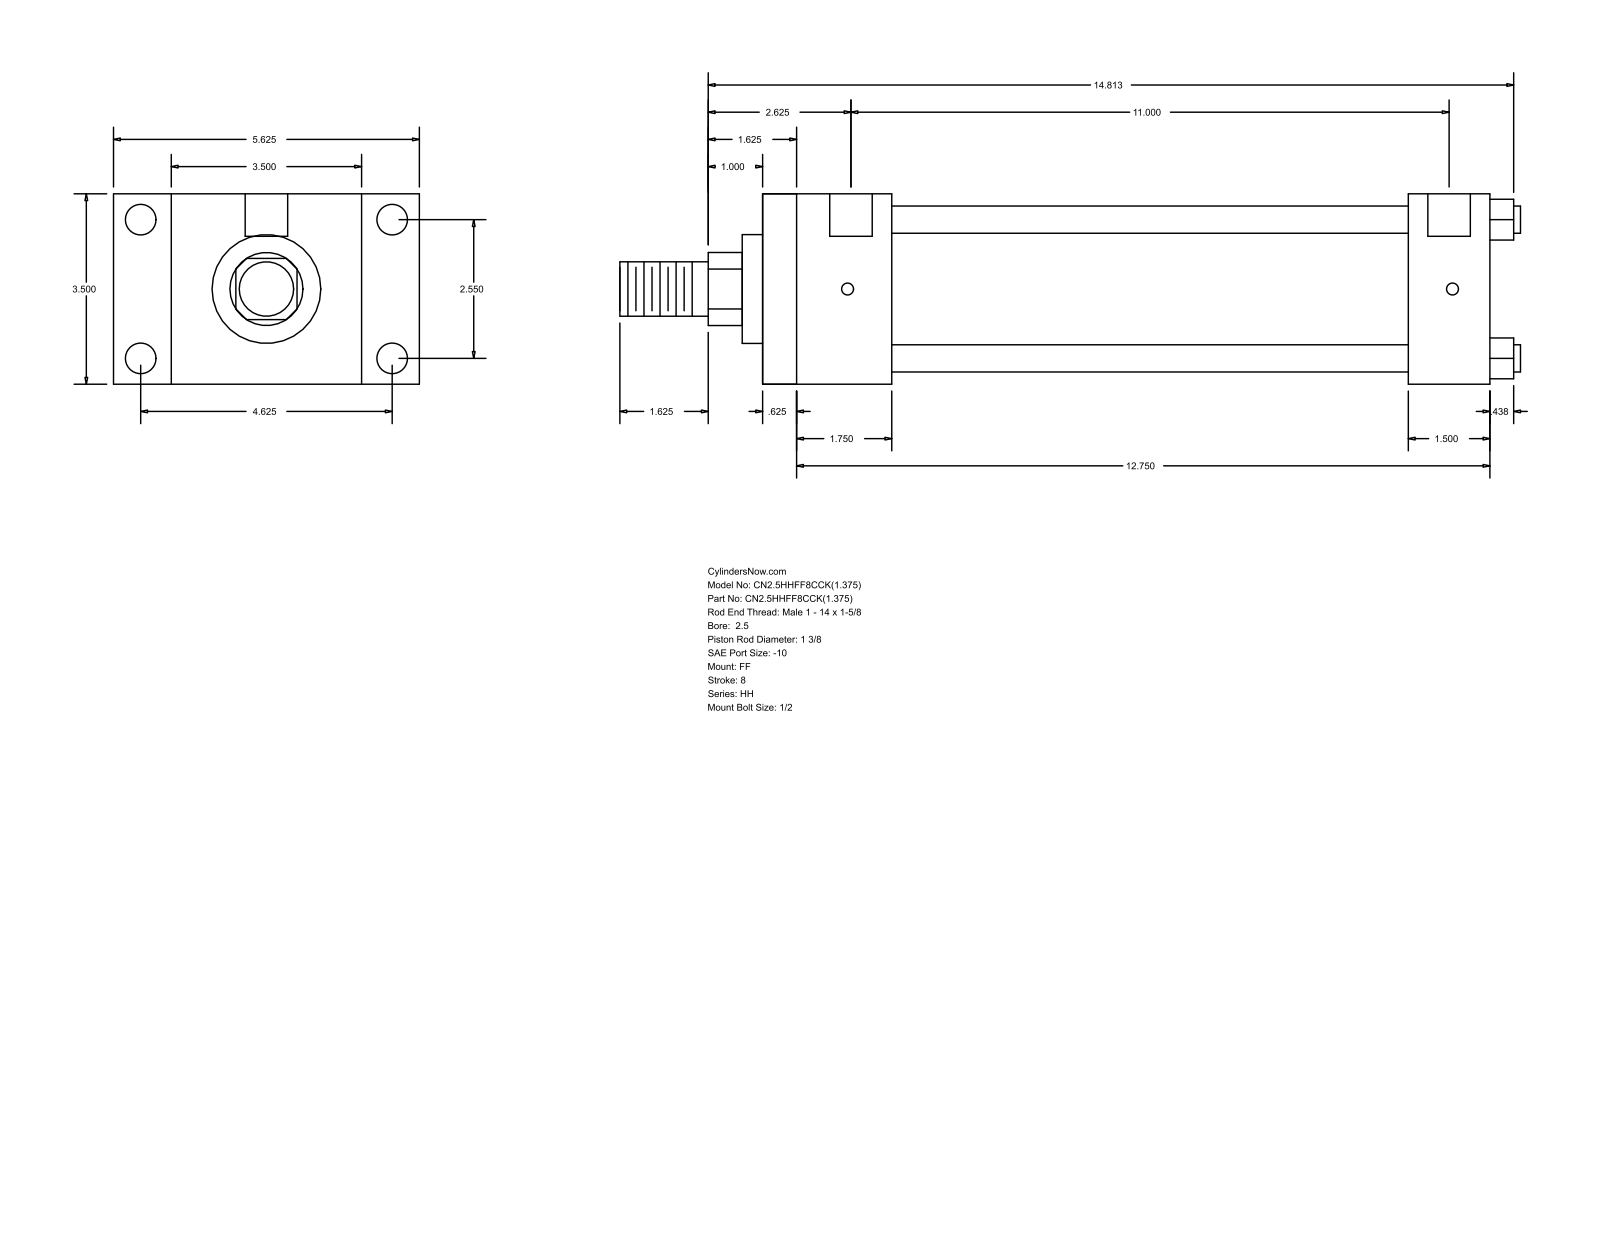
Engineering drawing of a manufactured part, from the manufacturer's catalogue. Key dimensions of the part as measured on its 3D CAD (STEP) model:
Part name (STEP PRODUCT): HH_FF__0250_1.375
STEP written by: GSSL Pune (CONFIG_CONTROL_DESIGN)
Units: millimetres
Bodies: 0 solids, 92 faces (64 planar, 28 cylindrical, 0 other)
Overall size (bounding box): 420.69 × 142.88 × 88.9
Round holes (diameter × count): ⌀5.56 ×4, ⌀14.3 ×4, ⌀19.84 ×2
Round bosses / shafts (diameter × count): ⌀12.7 ×4, ⌀73.03 ×1, ⌀50.8 ×1, ⌀34.92 ×1, ⌀25.4 ×1
Partial cylindrical surfaces — rounded edges, fillets, slot ends (radius × count): R17.06 ×1
Main face-to-face distances: 88.9, 339.72, 15.87, 323.85, 60.32, 44.45, 279.4, 301.62, 285.75, 241.3
Hole centre spacings: 64.76, 117.48, 134.15, 282.57, 1.58, 1.59, 279.4, 280.98
